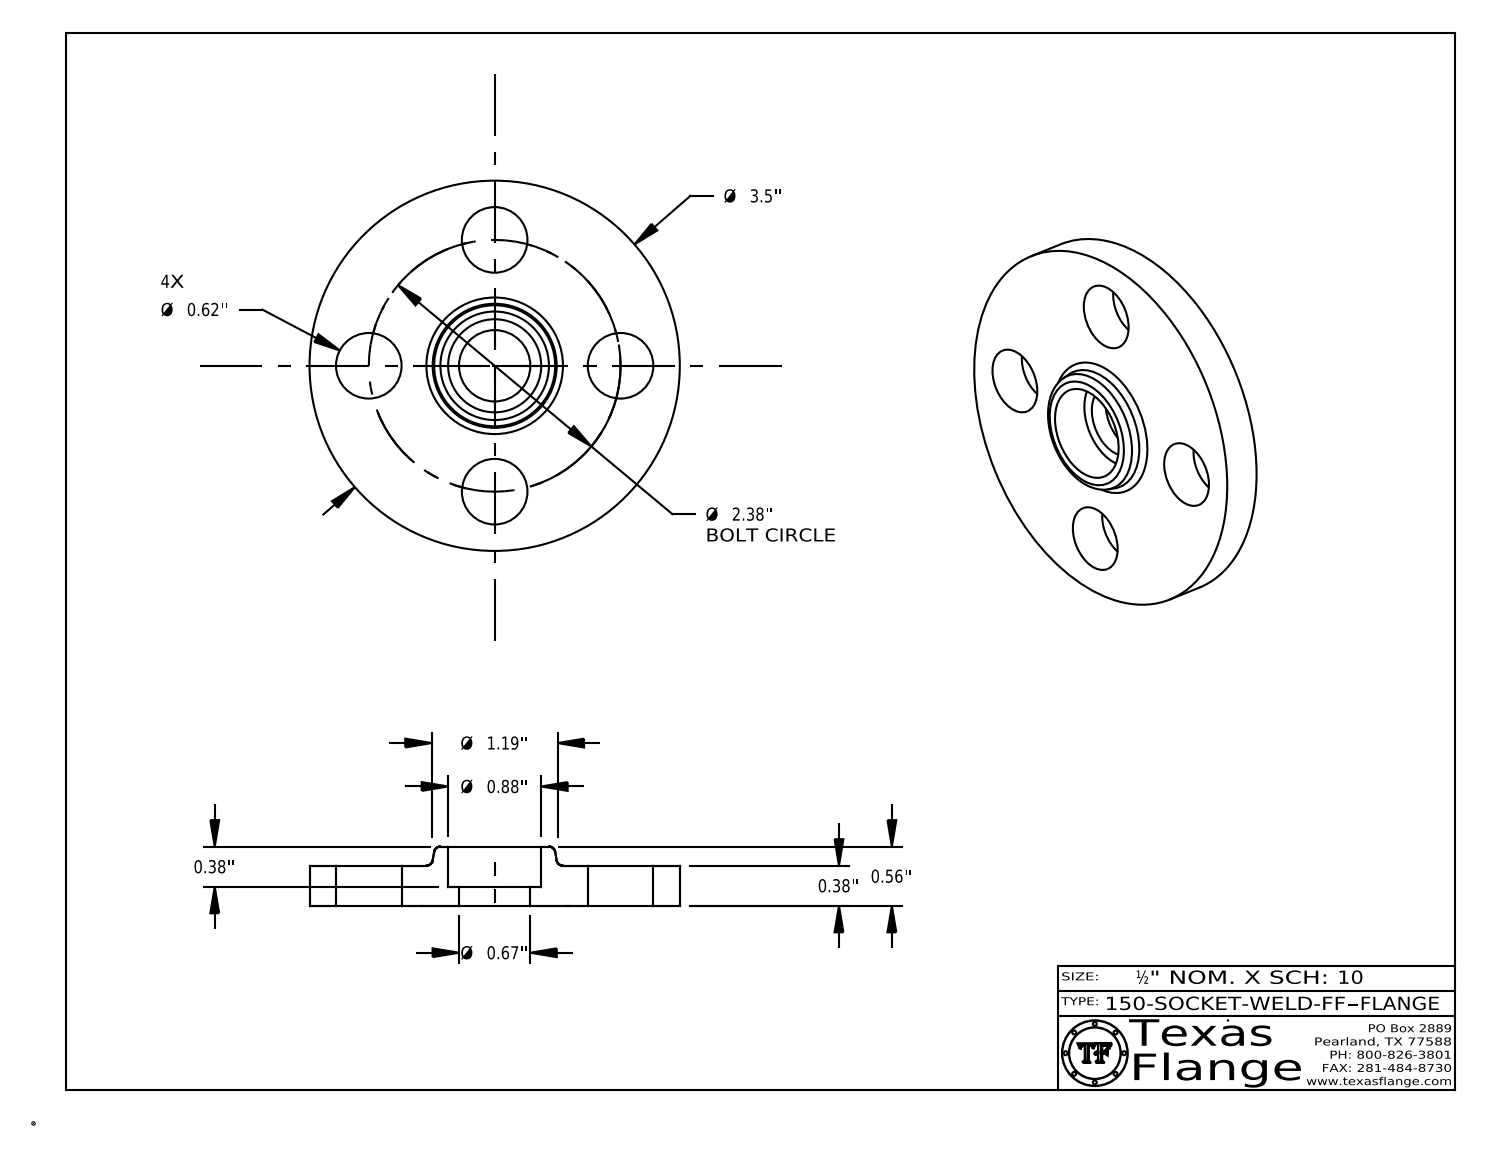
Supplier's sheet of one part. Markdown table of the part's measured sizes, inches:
| quantity | value |
| --- | --- |
| part name | 150-SOCKET-WELD-FF |
| STEP written by | CATIA V5 STEP AP214 (AUTOMOTIVE_DESIGN) |
| units | inches |
| bodies | 1 solid, 410 faces (370 planar, 34 cylindrical, 6 other) |
| overall size | 3.5 × 3.5 × 0.56 |
| volume | 3.09 in³ |
| surface area | 25.2 in² |
| round holes (diameter × count) | 0.62 × 4, 0.495 × 1, 0.674 × 1, 0.88 × 1 |
| round bosses / shafts (diameter × count) | 0.03 × 8, 3.5 × 1, 0.39 × 1 |
| main face-to-face distances | 0.38, 0.18, 0.2, 0.56, 0.365, 0.185, 0.015, 0.195, 0.148, 0.145 |
| hole center spacings | 1.19, 1.683, 0.911, 2.199, 2.38, 1.19 |
